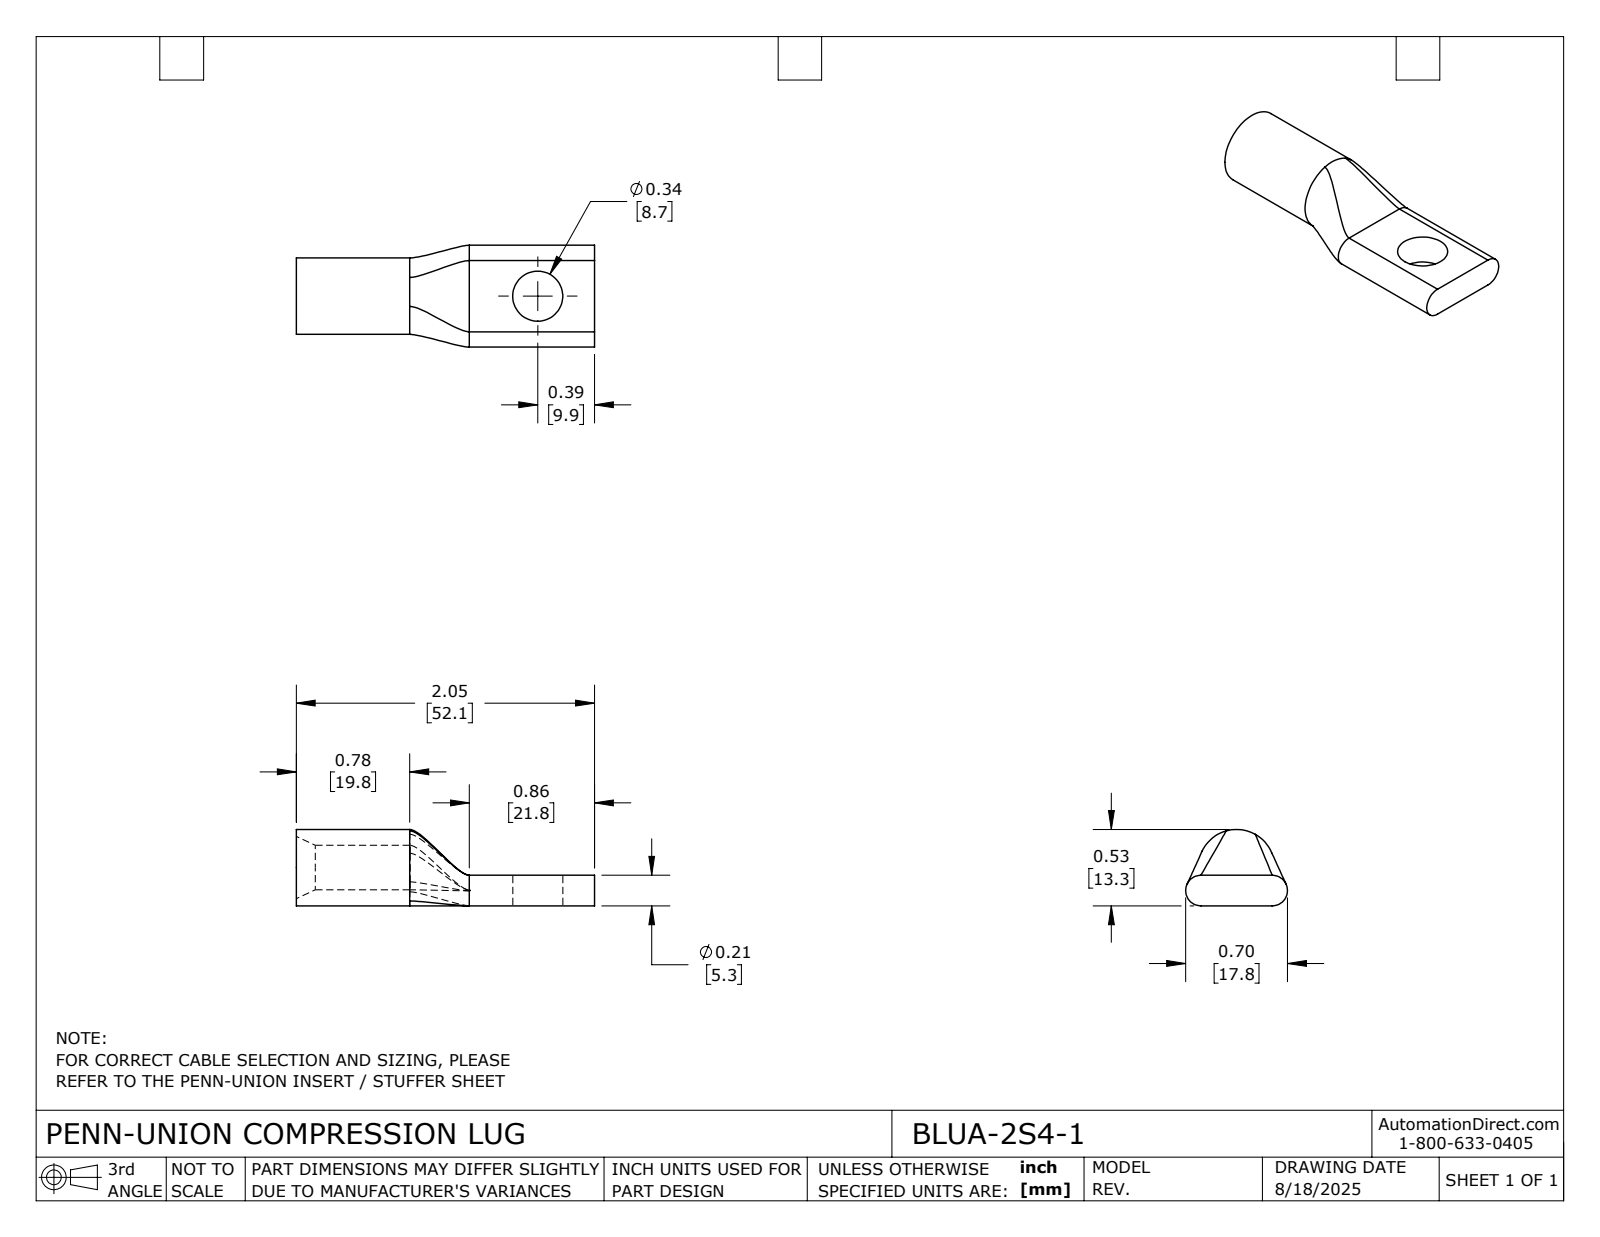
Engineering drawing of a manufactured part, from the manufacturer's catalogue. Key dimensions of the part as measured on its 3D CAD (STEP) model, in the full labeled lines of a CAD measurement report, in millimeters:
Part name (STEP PRODUCT): BLUA-2S4-1
STEP written by: SolidWorks 2024 (CONFIG_CONTROL_DESIGN)
Units: millimetres
Bodies: 1 solid, 24 faces (5 planar, 9 cylindrical, 10 other)
Overall size (bounding box): 52.1 × 17.8 × 13.3
Volume: 4 310 mm³ · Surface area: 3 157 mm²
Round holes (diameter × count): ⌀7.8 ×1, ⌀8.7 ×1
Round bosses / shafts (diameter × count): ⌀13.3 ×1
Partial cylindrical surfaces — rounded edges, fillets, slot ends (radius × count): R2.7 ×2
Main face-to-face distances: 5.3, 52.1, 30.2, 21.8
